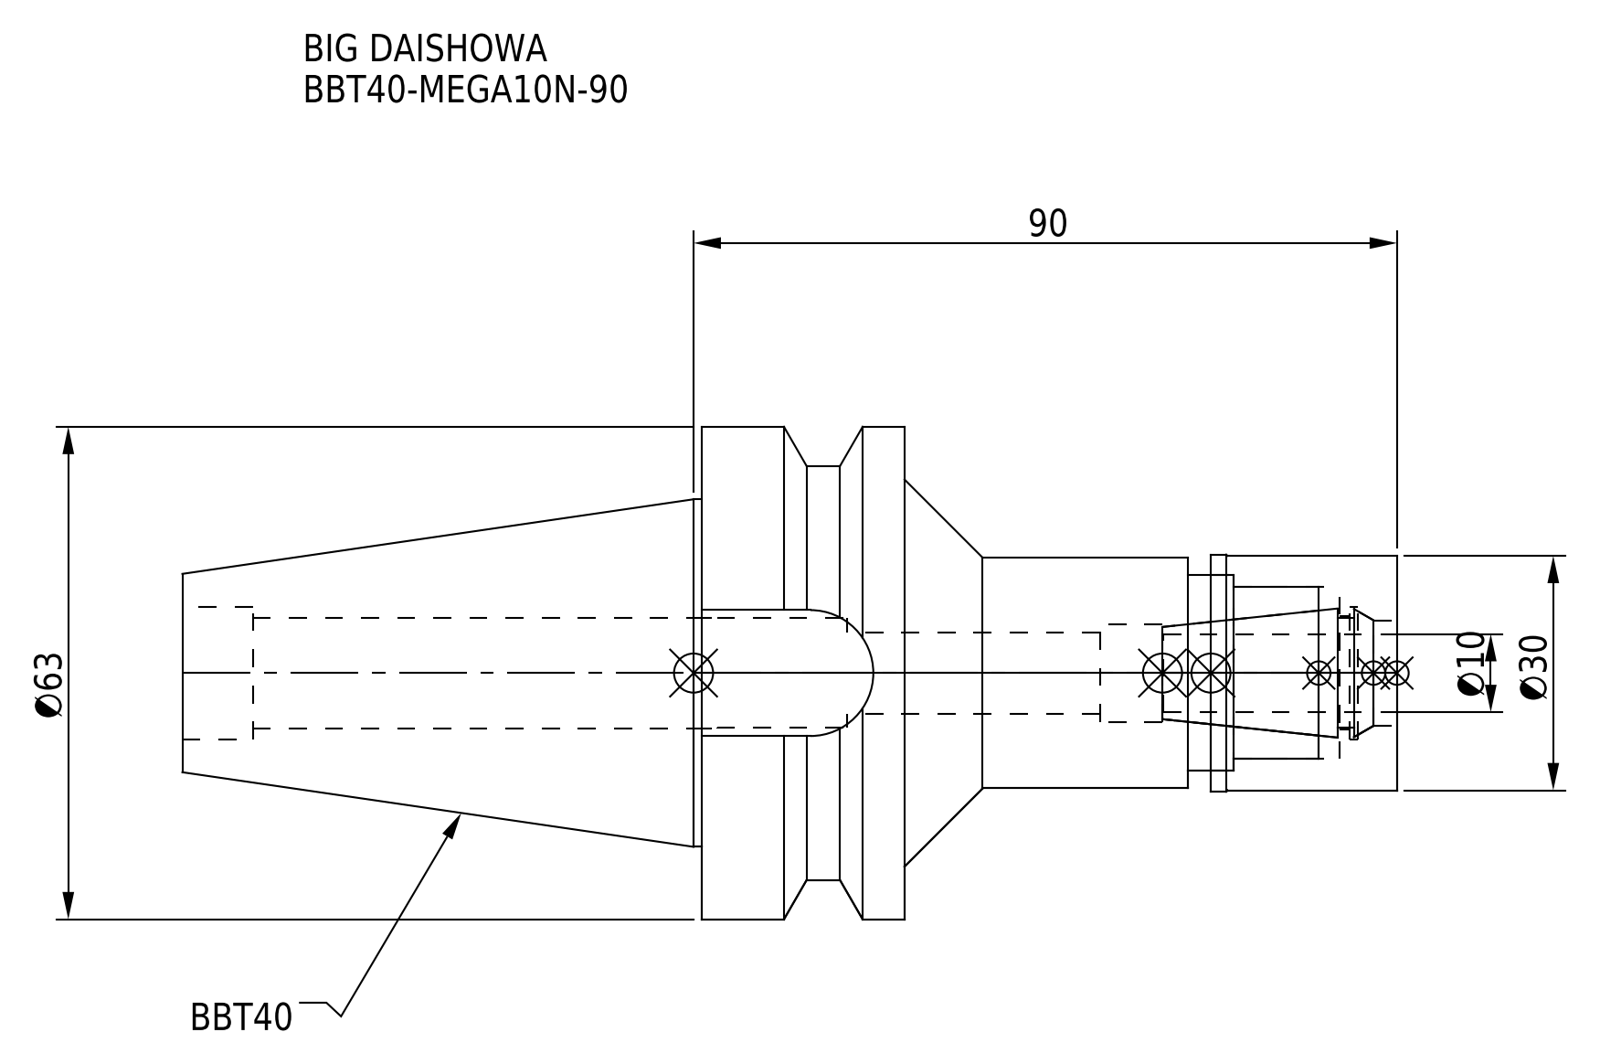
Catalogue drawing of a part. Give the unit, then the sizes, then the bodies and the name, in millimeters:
Units: millimetres
Overall size (bounding box): 155.4 × 63 × 63
Round holes (diameter × count): ⌀10.4 ×1, ⌀12.5 ×1, ⌀13.5 ×1, ⌀14 ×1, ⌀14.1 ×1, ⌀14.2 ×1, ⌀14.5 ×1, ⌀17 ×1, ⌀22 ×1, ⌀25 ×1
Round bosses / shafts (diameter × count): ⌀63 ×1, ⌀53 ×1, ⌀44.45 ×1, ⌀30.3 ×1, ⌀30 ×1, ⌀29.5 ×1
Partial cylindrical surfaces — rounded edges, fillets, slot ends (radius × count): R8.05 ×1
Main face-to-face distances: 26, 63, 89, 45, 155.4, 92.4, 66.4, 23.8, 39.2, 65.2
Volume: 161 302 mm³ · Surface area: 33 824 mm²
Bodies: 2 solids, 80 faces (24 planar, 42 cylindrical, 14 other)
Part name (STEP PRODUCT): BBT40-MEGA10N-90-100-FreeParts; BBT40-MEGA10N-90-100.stp; BBT40-MEGA10N-90_1.stp; BBT40MN10090-100_ASM.stp (+3 more)
STEP written by: SolidWorks 2019 (CONFIG_CONTROL_DESIGN)
